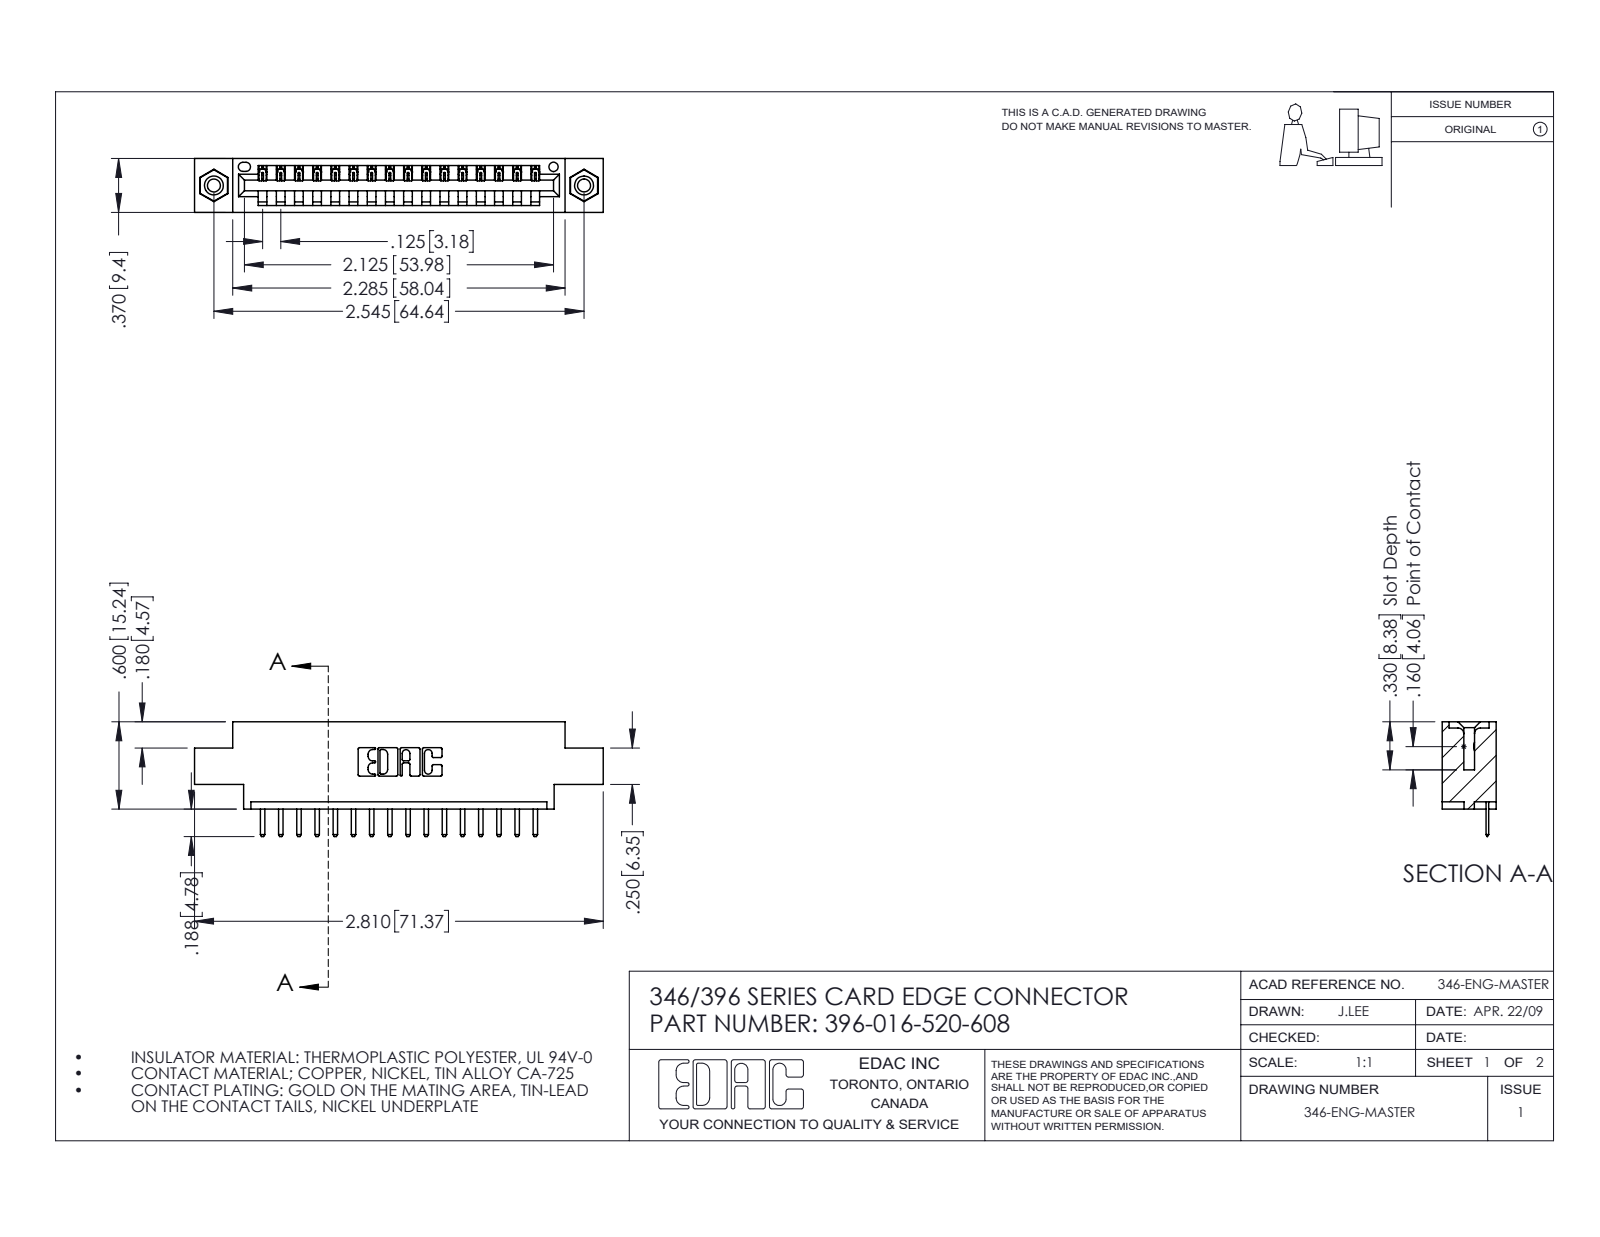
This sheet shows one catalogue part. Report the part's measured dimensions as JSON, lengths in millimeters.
{"part_name": "346 Part_0.170 Offset - 0.156 Dia-TI; 396-016-520-608; 345-250-001_345-250-003-102; 345-292-001_345-293-120", "step_written_by": "SolidWorks 2016 (CONFIG_CONTROL_DESIGN)", "units": "millimeters", "bodies": {"solids": 19, "faces": 1178, "planar": 784, "cylindrical": 378, "other": 16}, "overall_size": [71.4, 20, 9.4], "volume_mm3": 6440, "surface_area_mm2": 7806, "round_holes": [[2.3, 2], [3.2, 2], [4, 2], [1.6, 1]], "round_bosses_or_shafts": [[3.9, 2]], "partial_cylinders_radius": [[0.3, 34], [0.2, 32], [0.3, 22], [0.2, 6], [0.8, 6], [0.7, 3], [0.8, 2], [1, 2]], "face_to_face_distances": [9.4, 1.2, 8.2, 6.4, 5.6, 3.8, 2.5, 4.4, 1.8, 7.6], "hole_center_spacings": [6.2, 59.4, 64.6]}
